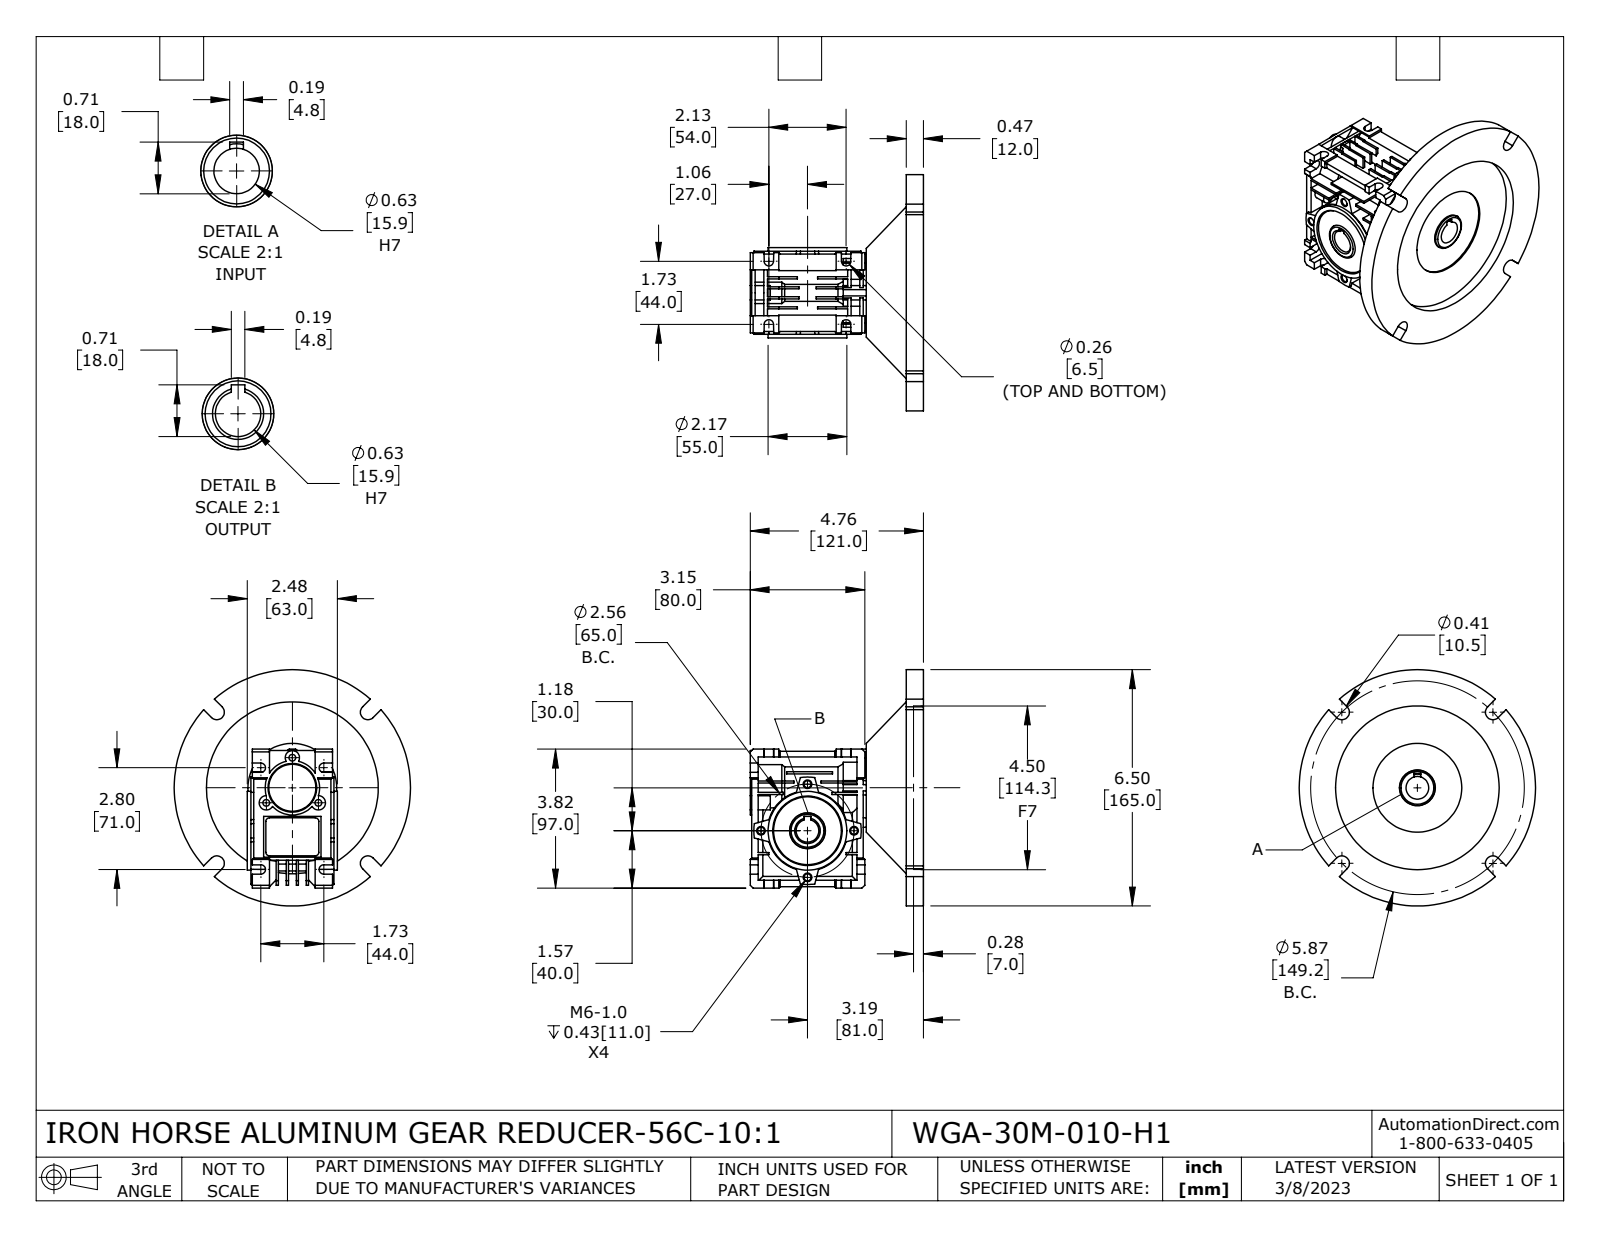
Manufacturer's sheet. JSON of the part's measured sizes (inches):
{"part_name": "WGA-30M-010-H1", "step_written_by": "SolidWorks 2021 (CONFIG_CONTROL_DESIGN)", "units": "inches", "bodies": {"solids": 1, "faces": 682, "planar": 442, "cylindrical": 168, "other": 72}, "overall_size": [6.496, 6.496, 4.764], "volume_in3": 39.8, "surface_area_in2": 198.1, "round_holes": [[0.194, 4], [0.194, 4], [0.183, 3], [0.625, 2], [2.441, 1], [4.5, 1]], "round_bosses_or_shafts": [[6.496, 1], [2.205, 1], [2.165, 1], [1.496, 1], [0.984, 1]], "partial_cylinders_radius": [[0.128, 8], [0.197, 7], [0.098, 4], [0.207, 4], [0.374, 1], [0.669, 1], [0.846, 1], [1.476, 1]], "face_to_face_distances": [0.276, 0.059, 0.039, 0.472, 0.217, 0.197, 0.177, 0.551, 0.335, 0.157], "hole_center_spacings": [1.28, 1.809, 0.827, 1.432, 2.559, 1.432]}
